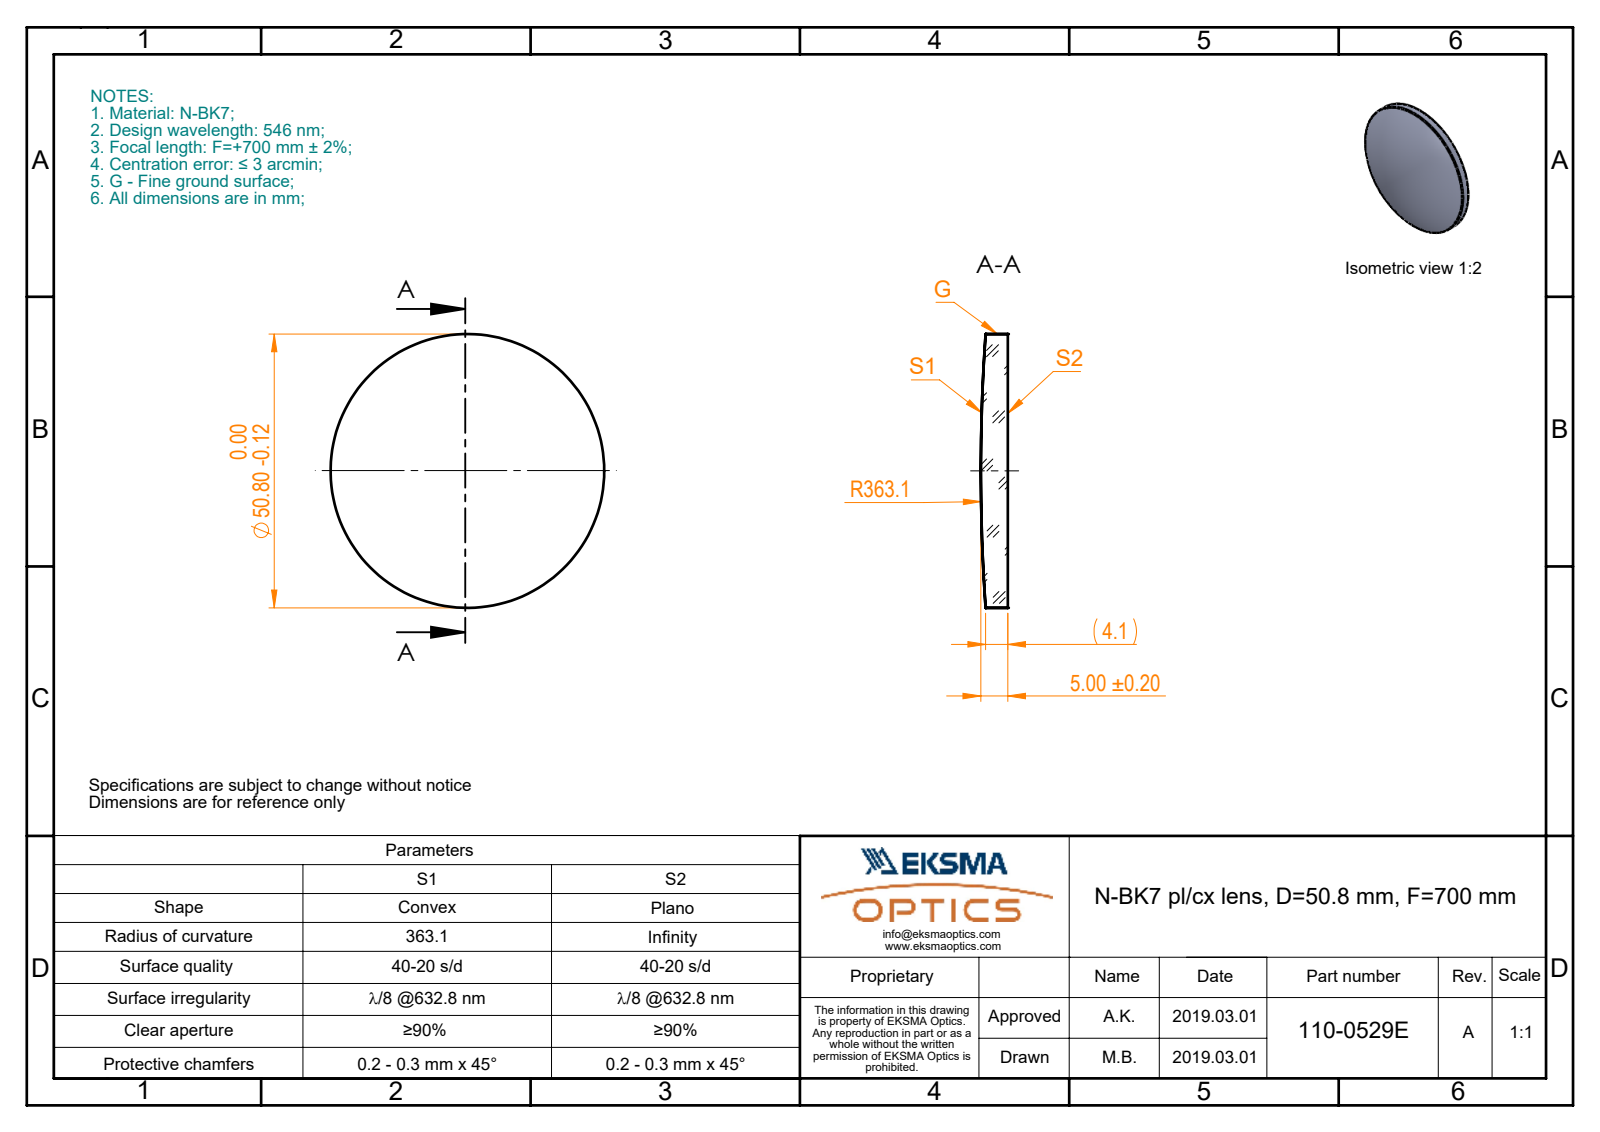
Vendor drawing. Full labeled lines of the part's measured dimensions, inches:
Part name (STEP PRODUCT): 110-0529E BK7 pl-cx 50.8 F700
STEP written by: SolidWorks 2017 (CONFIG_CONTROL_DESIGN)
Units: inches
Bodies: 1 solid, 5 faces (1 planar, 2 cylindrical, 2 other)
Overall size (bounding box): 2 × 2 × 0.197
Volume: 0.563 in³ · Surface area: 7.304 in²
Round bosses / shafts (diameter × count): ⌀2 ×1
